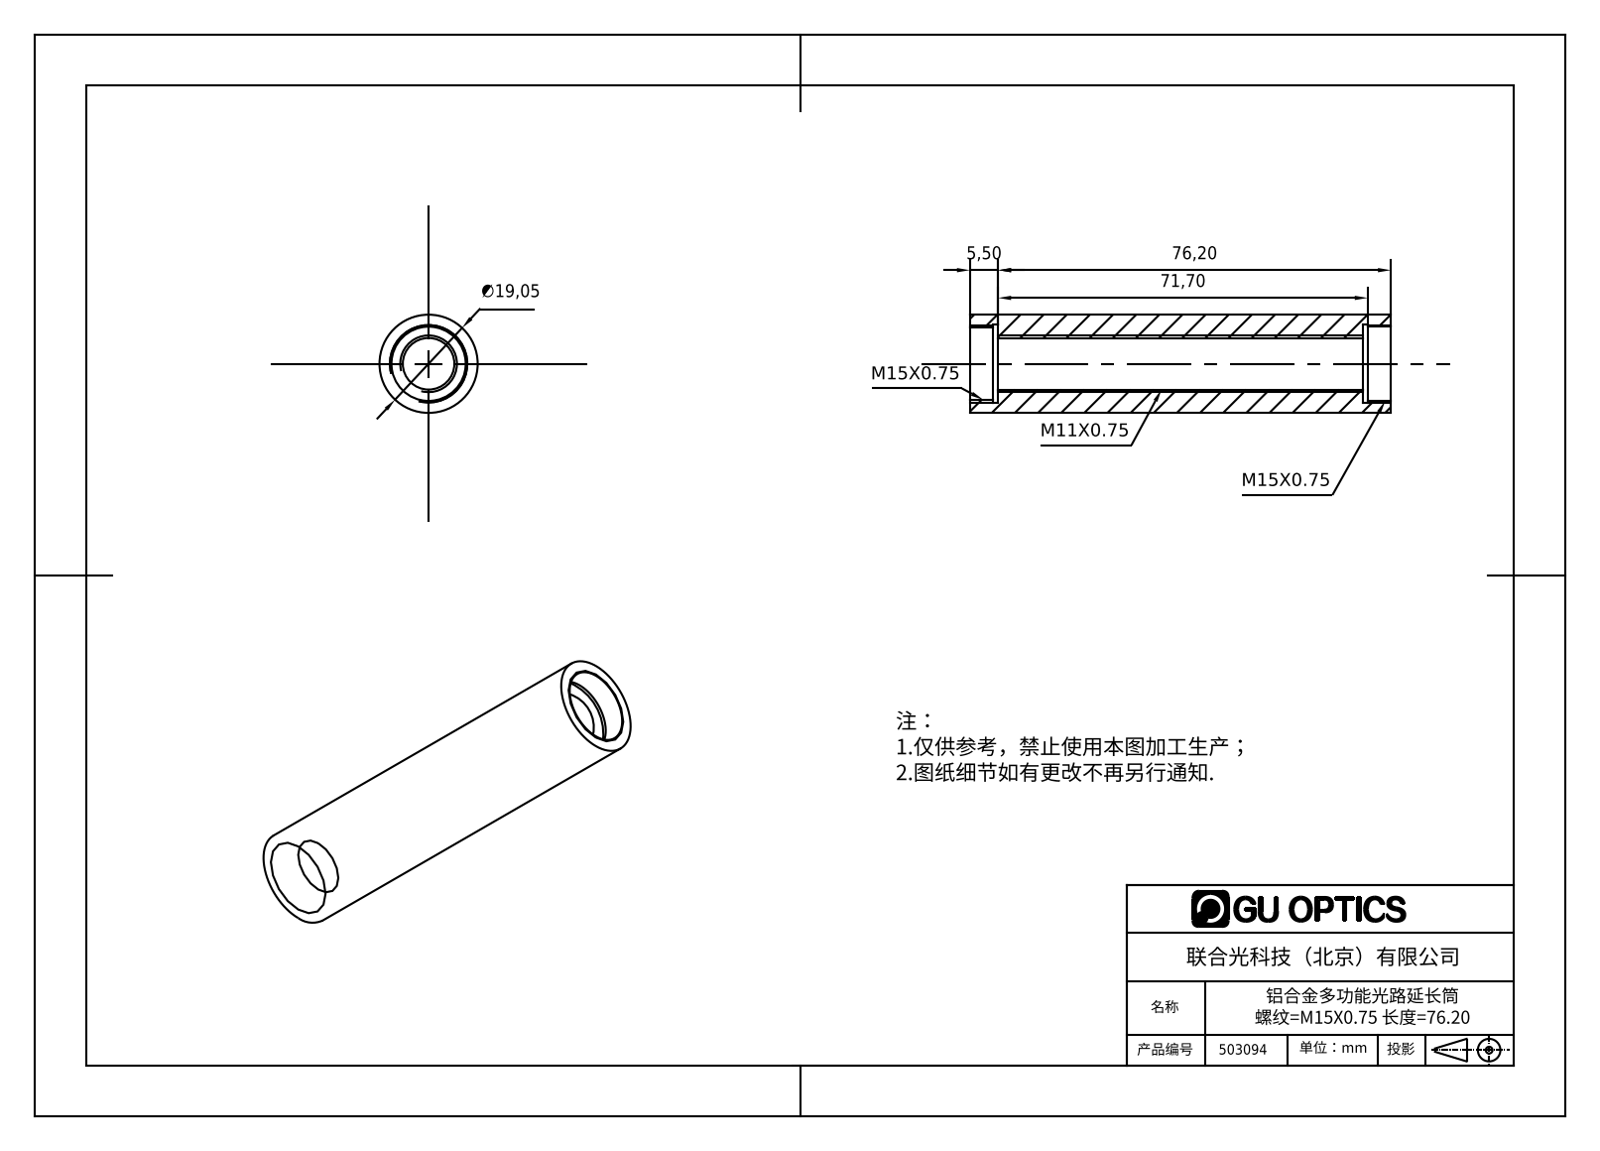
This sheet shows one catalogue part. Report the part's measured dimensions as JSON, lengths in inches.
{"part_name": "503094", "step_written_by": "SolidWorks 2016 (AUTOMOTIVE_DESIGN)", "units": "inches", "bodies": {"solids": 1, "faces": 18, "planar": 6, "cylindrical": 12, "other": 0}, "overall_size": [3.217, 0.75, 0.75], "volume_in3": 0.973, "surface_area_in2": 12.58, "round_holes": [[0.394, 1], [0.551, 1], [0.567, 1], [0.598, 1]], "round_bosses_or_shafts": [[0.75, 1]], "face_to_face_distances": [0.217, 3, 3.217, 2.783, 0.177, 3.039, 0.039, 2.823, 2.862]}
